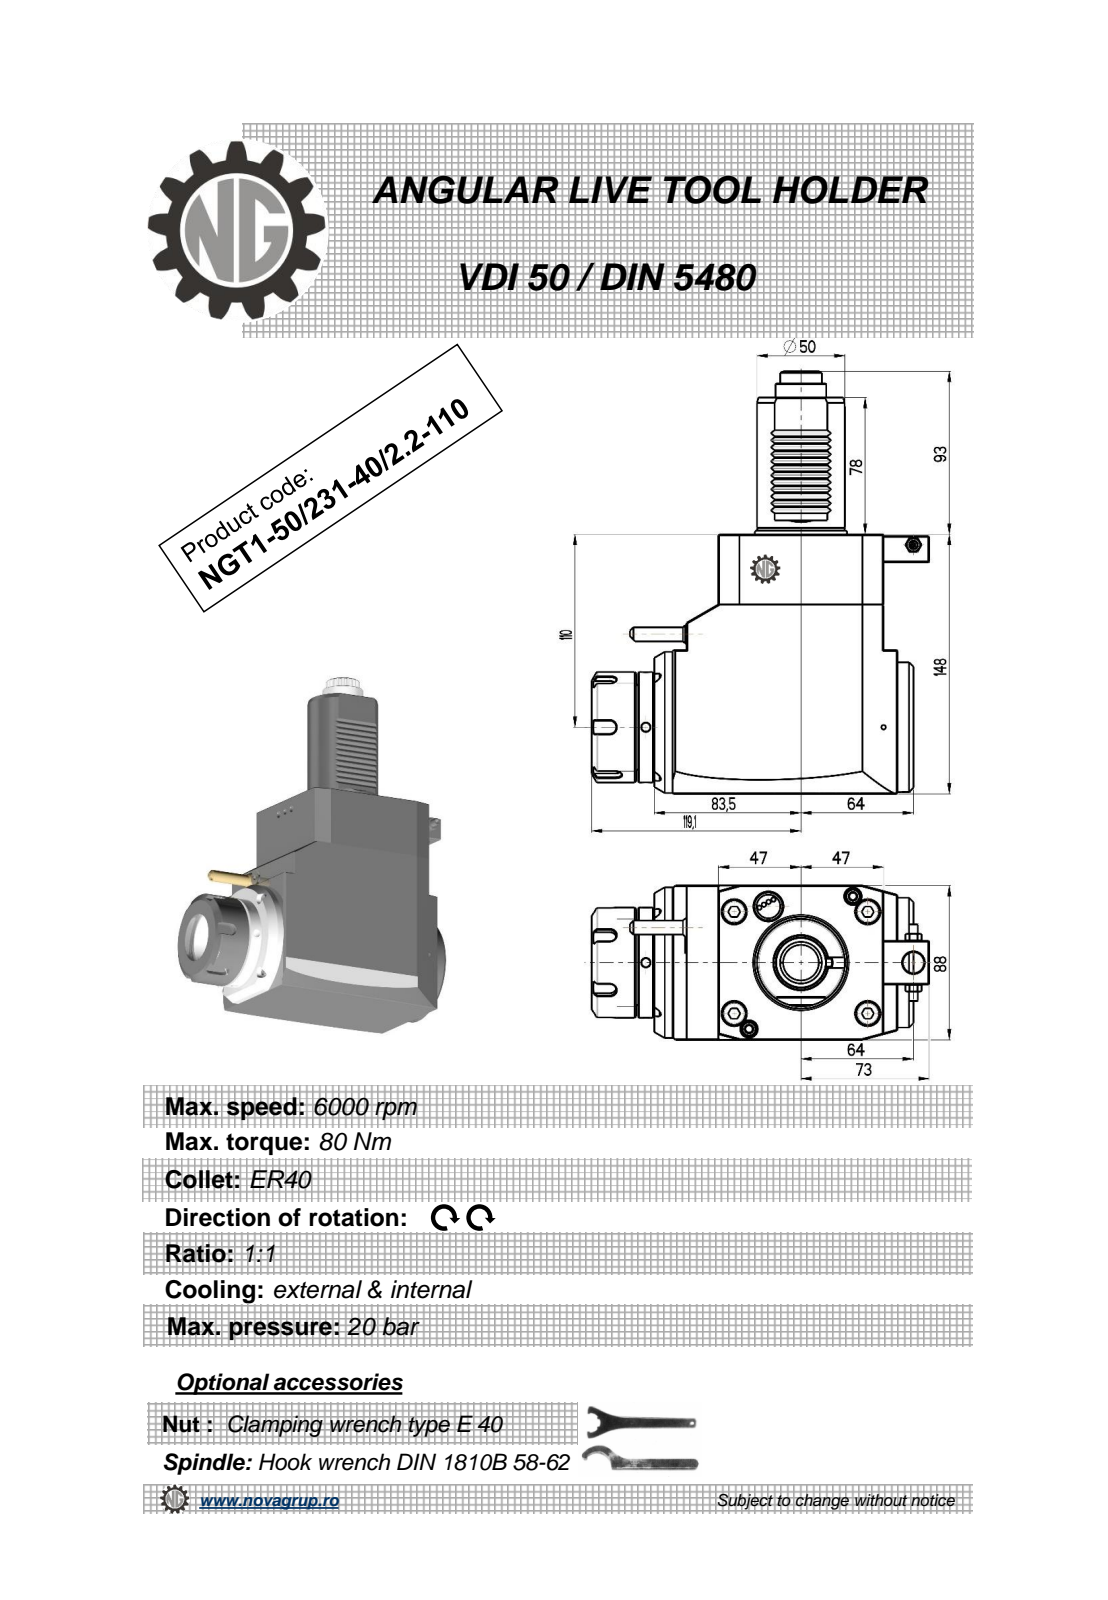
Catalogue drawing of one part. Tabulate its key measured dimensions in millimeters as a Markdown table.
| quantity | value |
| --- | --- |
| part name | NGT1_50_231_40_1_2_110 |
| STEP written by | PRO/ENGINEER BY PARAMETRIC TECHNOLOGY CORPORATION, 2010280 (CONFIG_CONTROL_DESIGN) |
| units | millimeters |
| bodies | 1 solid, 516 faces (206 planar, 161 cylindrical, 149 other) |
| overall size | 241 × 192.1 × 88 |
| volume | 1 842 000 mm³ |
| surface area | 114 530 mm² |
| round holes (diameter × count) | 5 × 3, 3 × 1, 4.2 × 1, 9.5 × 1, 12 × 1, 33.5 × 1 |
| round bosses / shafts (diameter × count) | 86 × 1, 74 × 1, 63 × 1, 51 × 1, 50 × 1, 28.8 × 1, 10 × 1, 8.96 × 1 |
| partial cylindrical surfaces (radius × count) | 3.04 × 36, 0.26 × 12, 0.3 × 12, 0.2 × 6, 3.75 × 5, 10.56 × 1, 11.88 × 1, 17.5 × 1 |
| main face-to-face distances | 88, 148, 94, 147.5, 17, 8, 9, 111, 120, 36.5 |
| hole center spacings | 52.46, 56.65, 101.5, 152.25, 184.38 |
